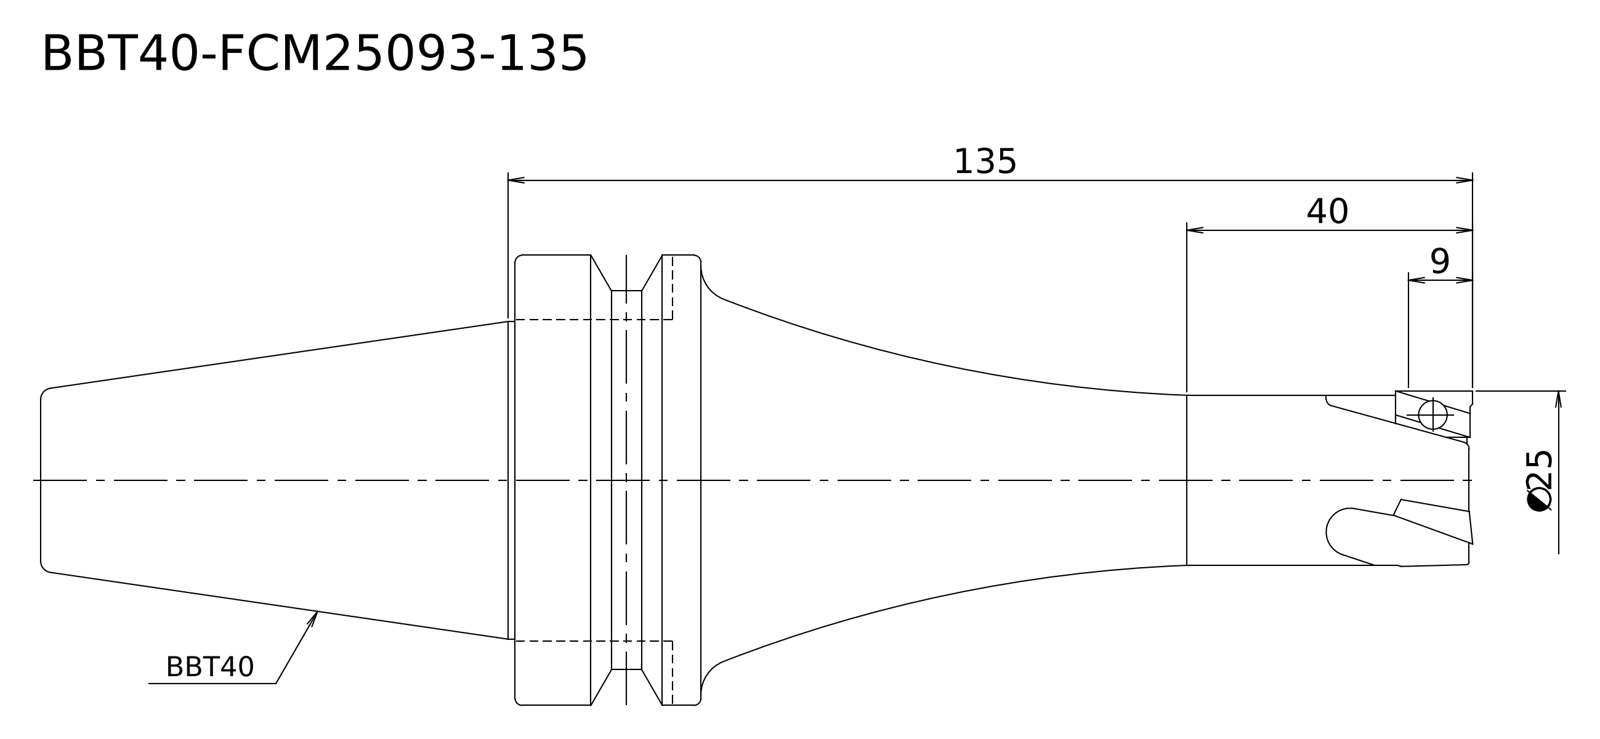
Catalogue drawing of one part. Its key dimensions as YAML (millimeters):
step_written_by: "Kubotek KeyCreator V8.5.1 (14335) (CONFIG_CONTROL_DESIGN)"
units: millimeters
bodies: {solids: 1, faces: 17, planar: 4, cylindrical: 6, other: 7}
overall_size: [200.4, 63, 63]
volume: 239437
surface_area: 27956
round_bosses_or_shafts:
  - {diameter: 63, count: 1}
  - {diameter: 53, count: 1}
  - {diameter: 44.45, count: 1}
  - {diameter: 25, count: 1}
  - {diameter: 23.8, count: 1}
face_to_face_distances: [66.4, 134, 200.4, 108, 26, 92.4]
